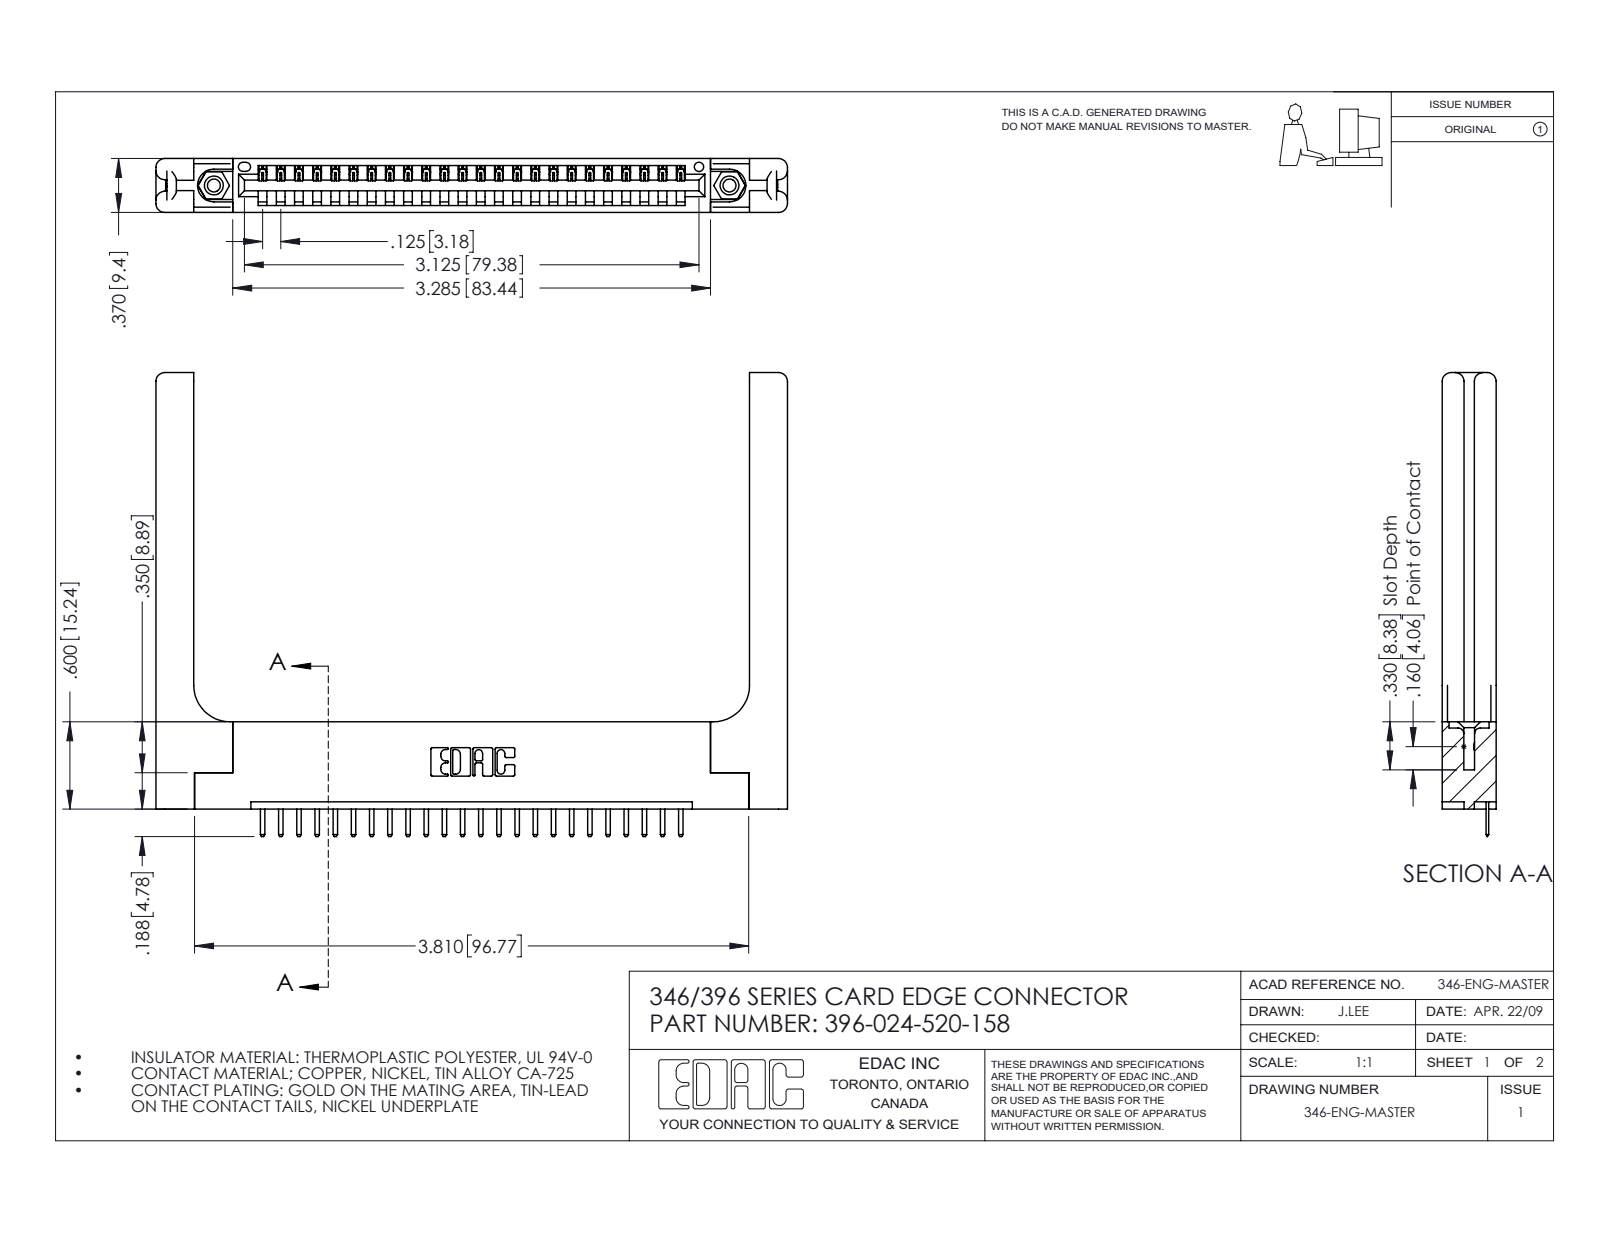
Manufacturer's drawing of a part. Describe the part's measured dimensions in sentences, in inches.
The part is named "345-292-001_345-293-120; 346-220-058_345-220-058; 396-024-520-158; 346 Part_Flush Mounting Lugs - 0.156 Dia-TH (+1 more)". Its 3-D file was written by "SolidWorks 2016 (CONFIG_CONTROL_DESIGN)". It is 29 solids with 1866 faces: 1232 planar, 574 cylindrical and 60 other. Overall it measures 4.341 by 3.188 by 0.37 inches. Its volume is 1.091 cubic inches and its surface area 27.43 square inches. Round holes: 2 of diameter 0.089, 2 of diameter 0.125, 2 of diameter 0.156, 1 of diameter 0.064. Round bosses or shafts: 2 of diameter 0.155. Partial cylindrical surfaces (rounded edges, fillets, slot ends): 50 of radius 0.01, 48 of radius 0.006, 22 of radius 0.01, 16 of radius 0.06, 6 of radius 0.007, 6 of radius 0.031, 3 of radius 0.026, 2 of radius 0.03. The main face-to-face distances are 0.37, 0.072, 0.15, 0.148, 0.048, 0.322, 0.25, 0.102, 0.22, 0.173. The hole center spacings are 0.246, 3.337, 3.545.
